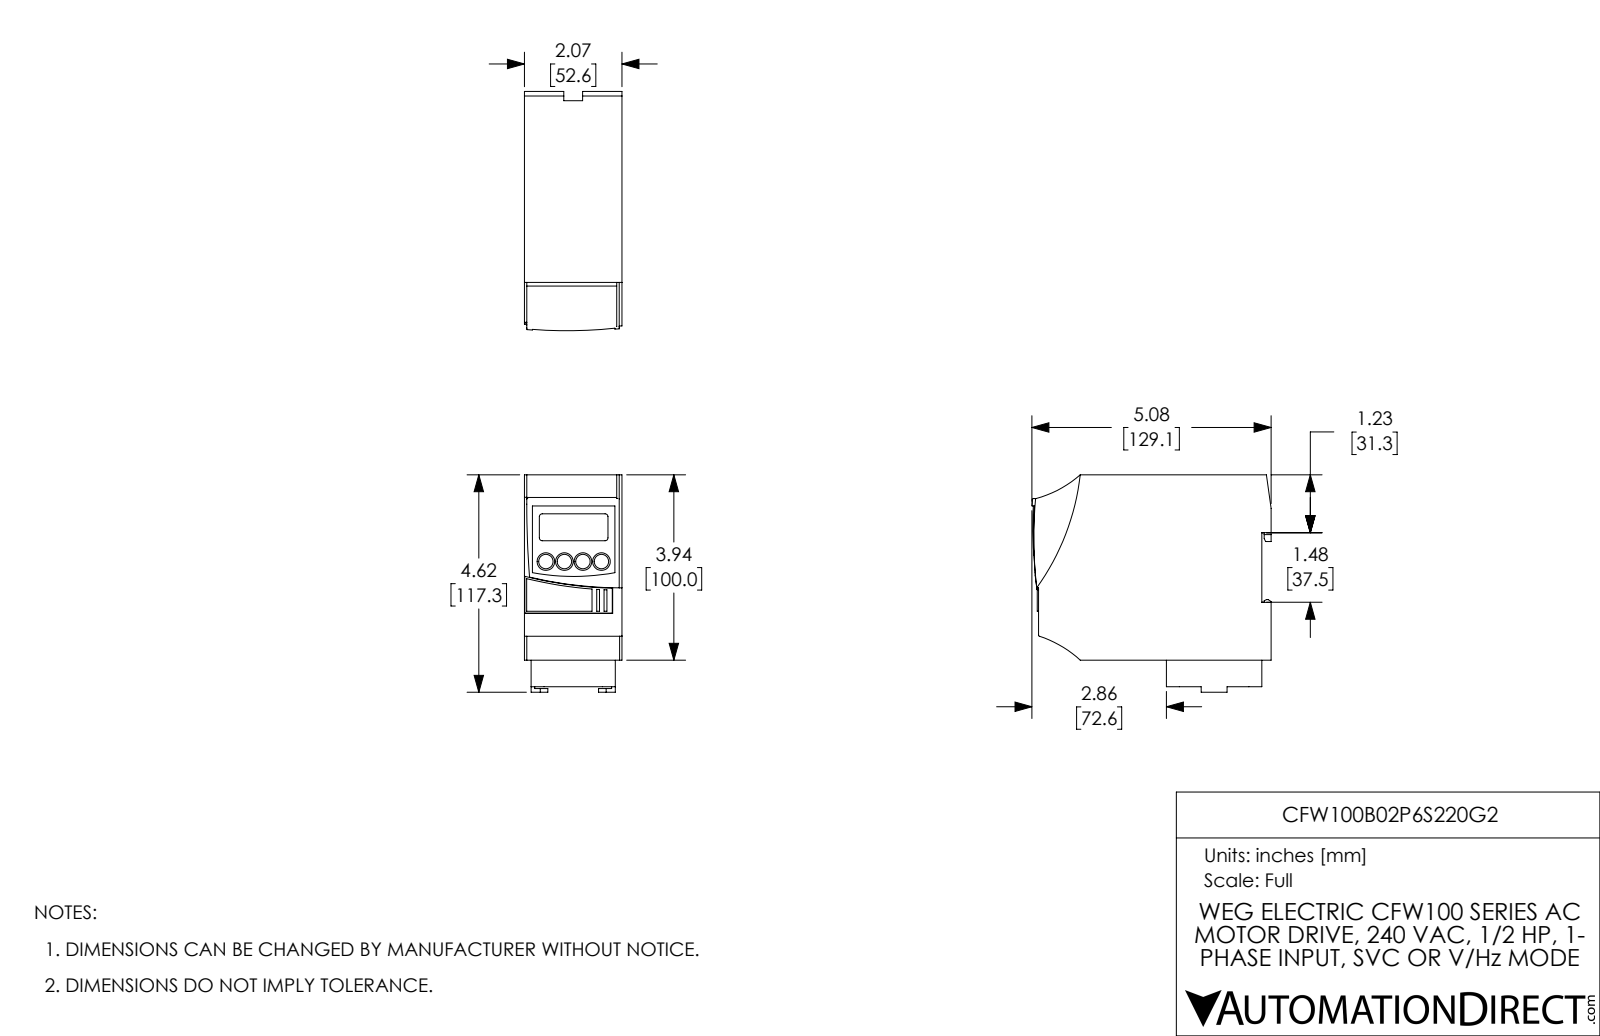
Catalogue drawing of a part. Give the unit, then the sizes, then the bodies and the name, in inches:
Units: inches
Overall size (bounding box): 5.082 × 4.618 × 2.073
Partial cylindrical surfaces — rounded edges, fillets, slot ends (radius × count): R0.059 ×4, R0.276 ×4, R2.362 ×2, R0.012 ×1, R0.02 ×1, R4.912 ×1, R5.118 ×1, R8.52 ×1
Main face-to-face distances: 2.072, 3.937, 0.563, 4.5, 0.197, 4.941, 4.744, 0.141, 1.932, 1.073
Volume: 39.86 in³ · Surface area: 82.59 in²
Bodies: 1 solid, 150 faces (118 planar, 22 cylindrical, 10 other)
Part name (STEP PRODUCT): CFW100B02P6S220G2
STEP written by: SolidWorks 2017 (AUTOMOTIVE_DESIGN)
